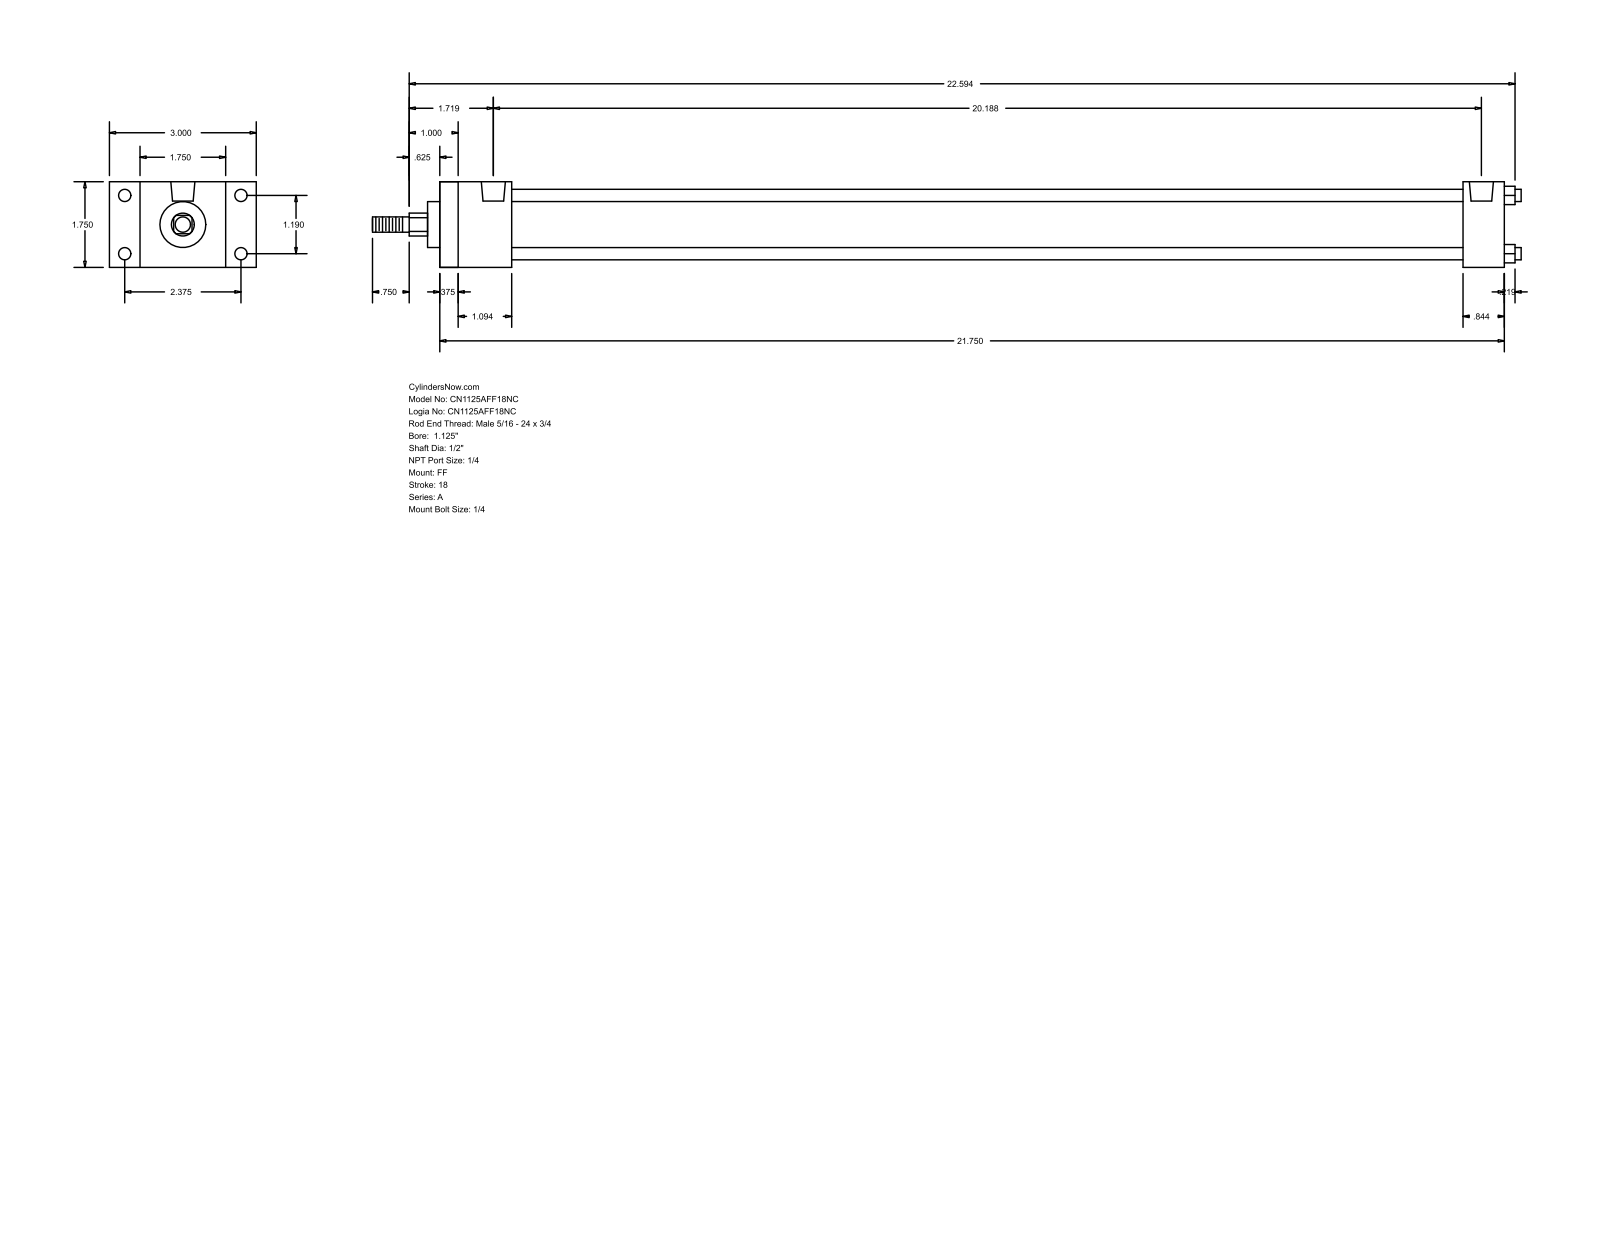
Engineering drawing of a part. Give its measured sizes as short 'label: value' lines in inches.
name: A_FF__0112_0.5
written by: GSSL Pune (CONFIG_CONTROL_DESIGN)
unit: in
bodies: 0 solids, 92 faces (64 planar, 28 cylindrical, 0 other)
size: 23.469 × 3 × 1.75
holes: 4× ⌀0.219, 4× ⌀0.25, 2× ⌀0.492
bosses: 4× ⌀0.25, 1× ⌀1.255, 1× ⌀0.937, 1× ⌀0.5, 1× ⌀0.313
rounds: 1× R0.234
face distances: 1.75, 21.75, 0.375, 21.375, 0.625, 20.906, 20.531, 0.844, 1.469, 1.094
hole spacings: 1.19, 2.375, 2.656, 20.063, 0.062, 0.063, 20.125, 20.125
